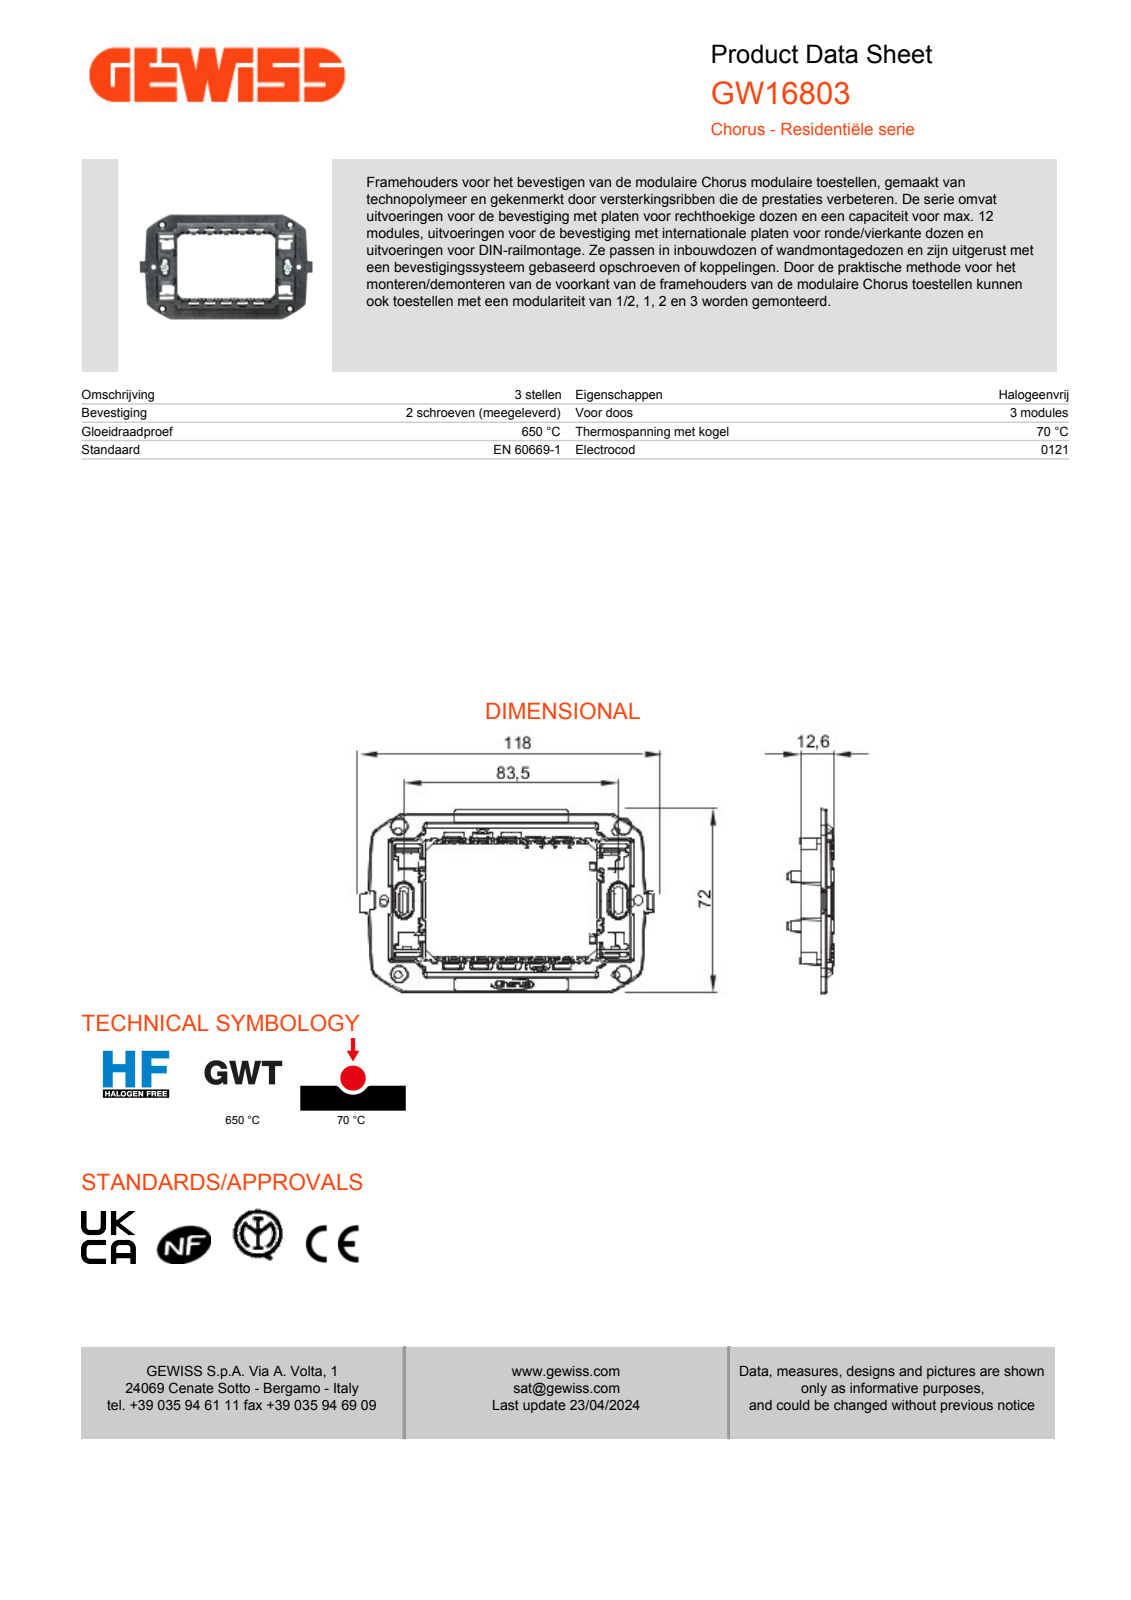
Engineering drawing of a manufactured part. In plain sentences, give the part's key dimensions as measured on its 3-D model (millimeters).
The part is named "Telaietto 3P NSC". Its 3-D file was written by "CATIA V5 STEP AP214 (AUTOMOTIVE_DESIGN)". It is 1 solid with 5718 faces: 2435 planar, 1258 cylindrical and 2025 other. Overall it measures 118 by 72 by 18.4 millimeters. Its volume is 12 920 cubic millimeters and its surface area 19 825 square millimeters. Round holes: 6 of diameter 3.1, 1 of diameter 2.8. Round bosses or shafts: 1 of diameter 3.2, 1 of diameter 3. Partial cylindrical surfaces (rounded edges, fillets, slot ends): 515 of radius 0.2, 134 of radius 0.5, 110 of radius 0.15, 106 of radius 0.3, 44 of radius 0.1, 20 of radius 1.5, 18 of radius 1, 12 of radius 0.6. The main face-to-face distances are 1.6, 2.2, 0.6, 68.82, 1, 1.4, 2, 11.1, 10.3, 1.5. The hole center spacings are 29.35, 97.44, 57.5, 87.2, 104.45, 24.35, 44.34, 63.31.
